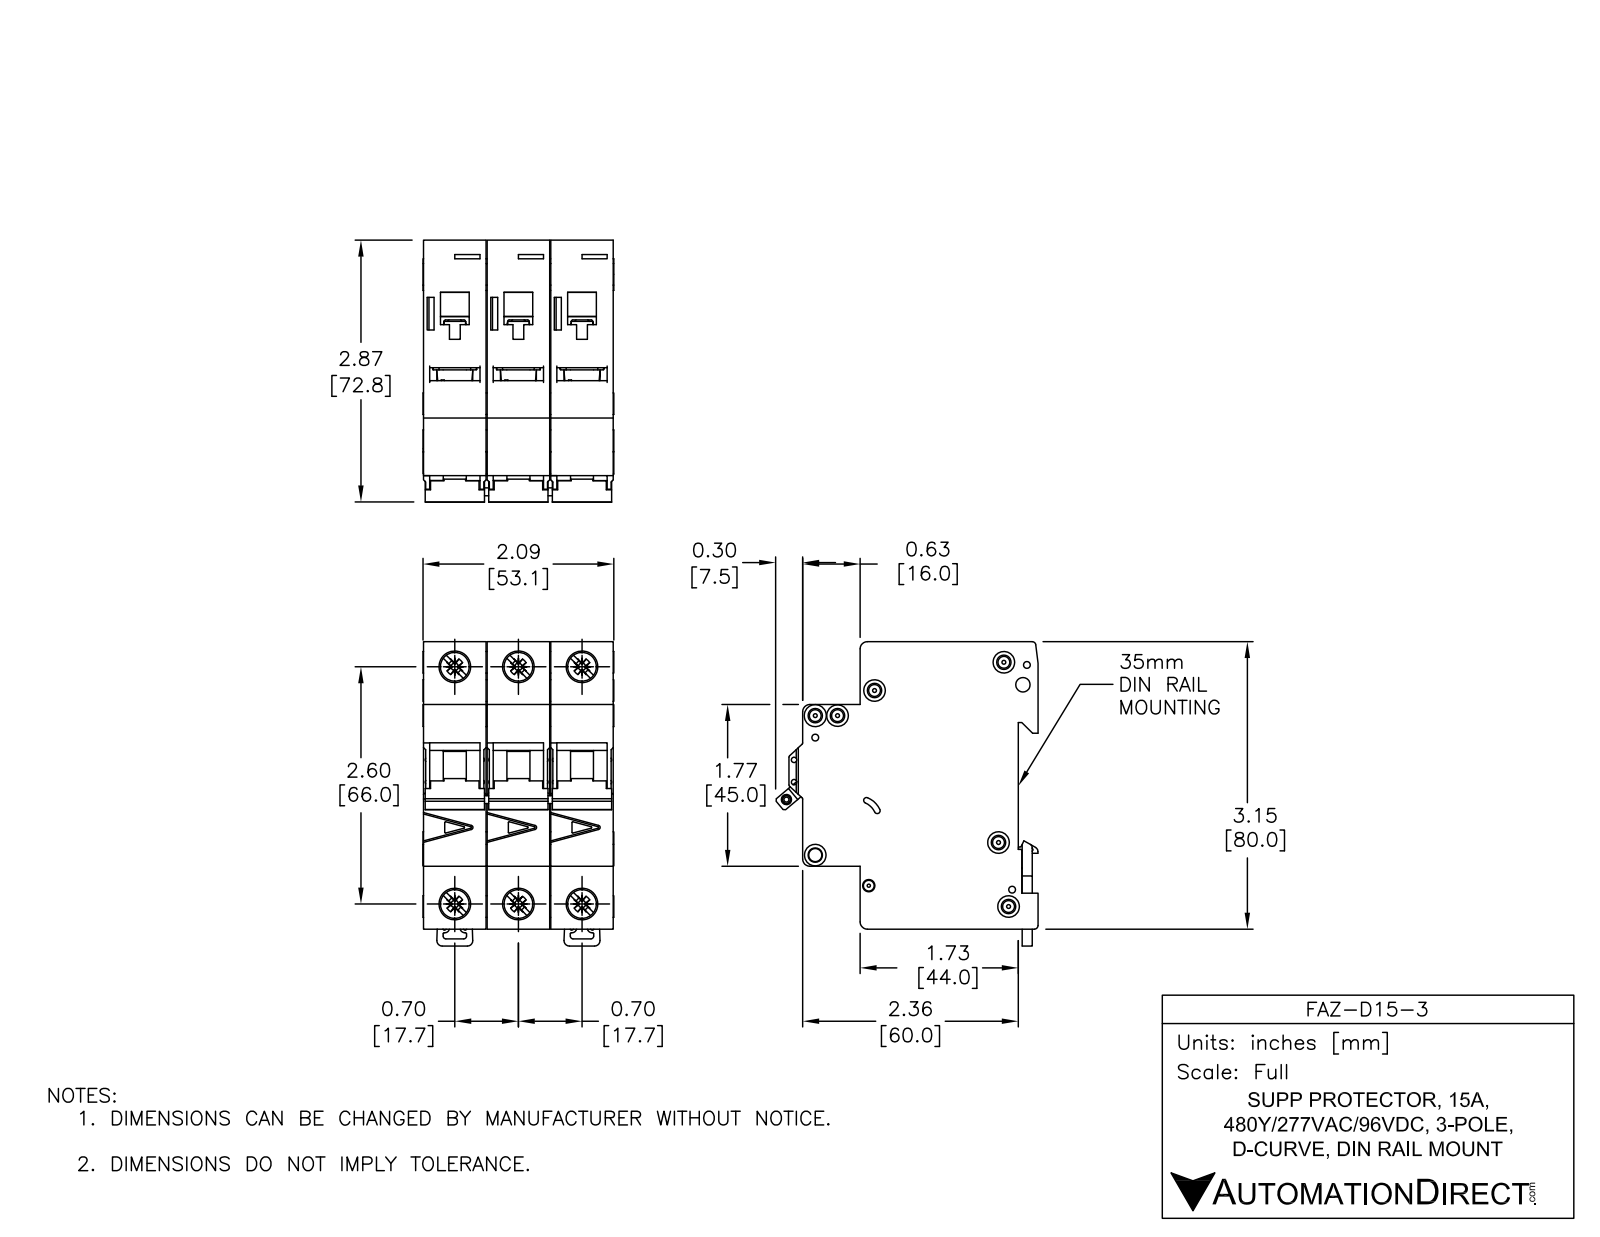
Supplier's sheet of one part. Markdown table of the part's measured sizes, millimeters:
| quantity | value |
| --- | --- |
| part name | FAZ-D15-3 |
| STEP written by | SolidWorks 2014 (AUTOMOTIVE_DESIGN) |
| units | millimeters |
| bodies | 11 solids, 1650 faces (697 planar, 590 cylindrical, 363 other) |
| overall size | 84.78 × 73.04 × 53.1 |
| volume | 224 680 mm³ |
| surface area | 58 052 mm² |
| round holes (diameter × count) | 3.6 × 6, 8.2 × 4, 1.9 × 3, 1.09 × 2, 1.5 × 2, 4 × 2, 7.15 × 2, 2.15 × 1, 2.2 × 1, 2.55 × 1, 3.3 × 1, 3.4 × 1 |
| round bosses / shafts (diameter × count) | 6 × 4, 2.5 × 3, 8.2 × 2 |
| partial cylindrical surfaces (radius × count) | 0.25 × 68, 0.5 × 25, 1 × 12, 2 × 12, 0.2 × 11, 1.8 × 3, 0.8 × 2, 3 × 2 |
| main face-to-face distances | 17.7, 17.5, 35.4, 35.2, 52.9, 17.9, 79.48, 5.5, 49.5, 44 |
| hole center spacings | 17.7, 68.33, 66, 6.2, 13.64, 35.4, 74.89, 4.81 |
